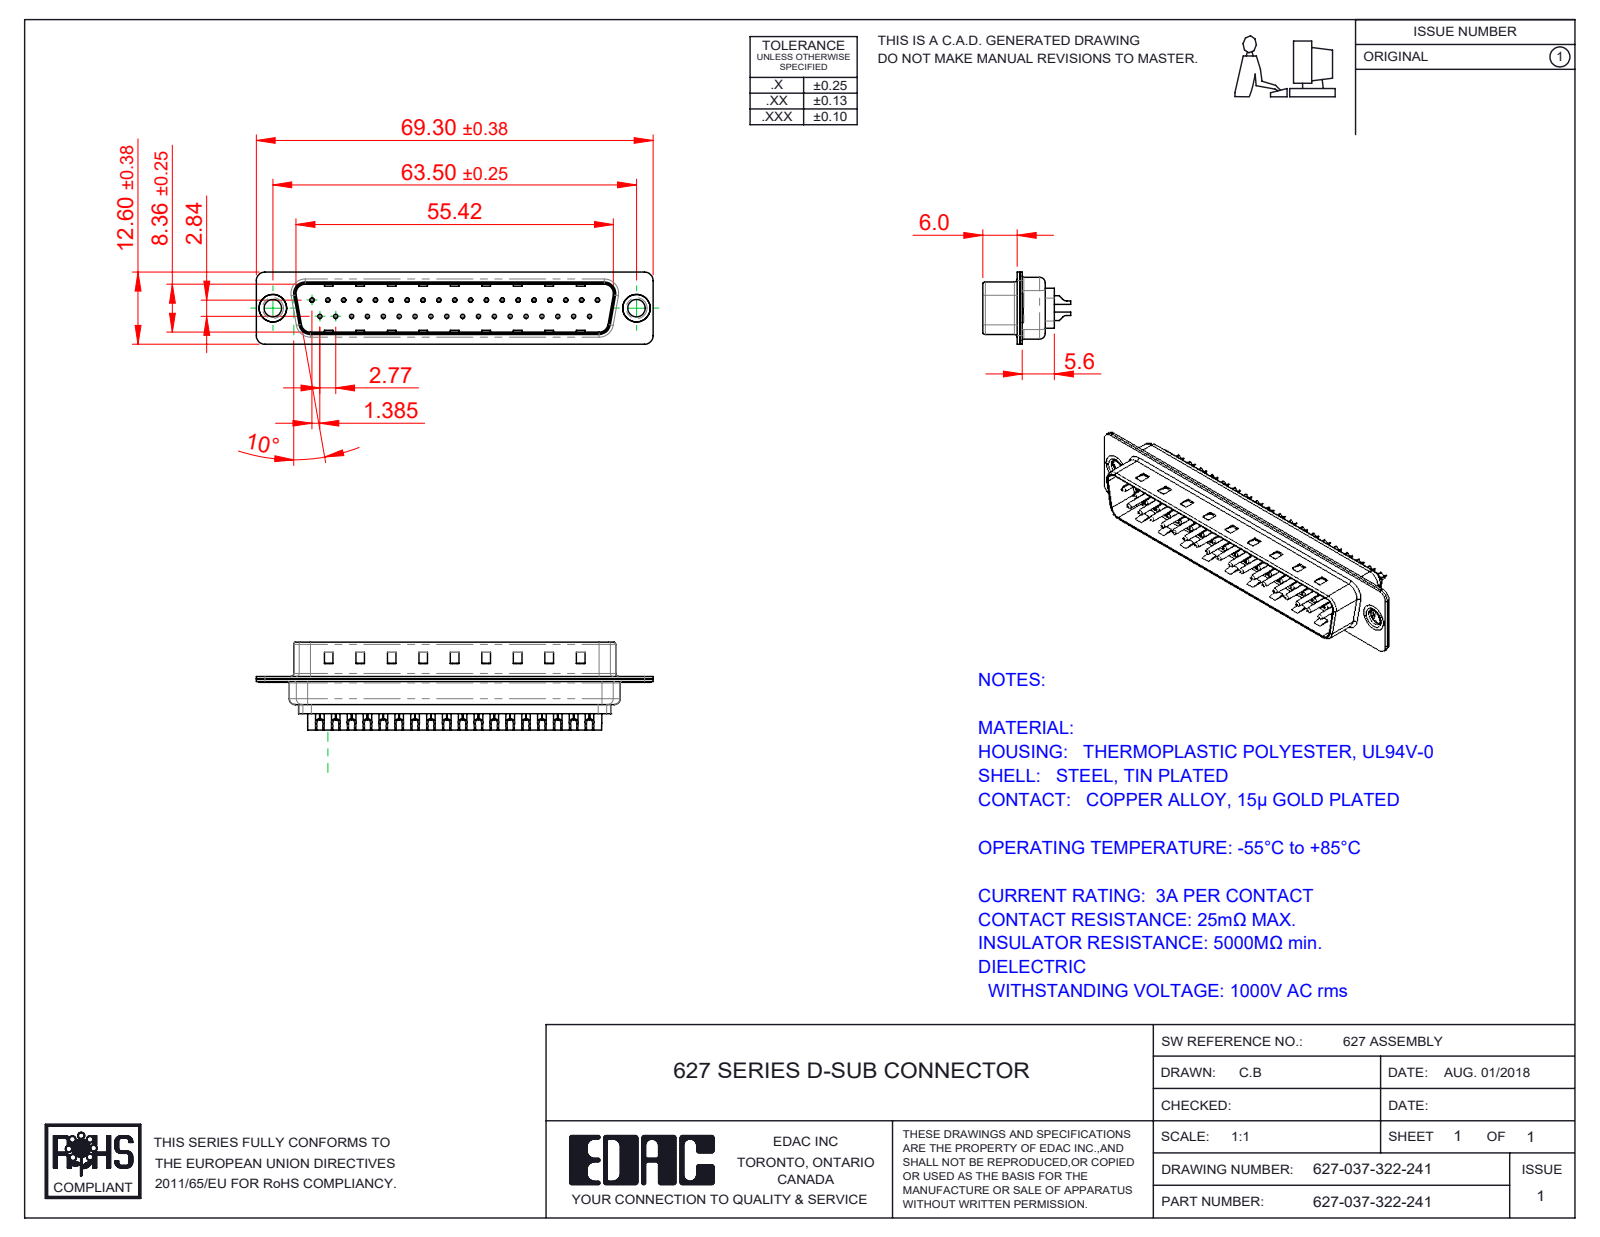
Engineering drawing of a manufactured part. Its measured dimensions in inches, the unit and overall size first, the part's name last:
Units: inches
Overall size (bounding box): 2.728 × 0.604 × 0.496
Round holes (diameter × count): ⌀0.014 ×37, ⌀0.043 ×37, ⌀0.063 ×37, ⌀0.12 ×2, ⌀0.157 ×2, ⌀0.189 ×2
Round bosses / shafts (diameter × count): ⌀0.079 ×37, ⌀0.059 ×37, ⌀0.03 ×37, ⌀0.197 ×2, ⌀0.193 ×2, ⌀0.14 ×2
Partial cylindrical surfaces — rounded edges, fillets, slot ends (radius × count): R0.059 ×16, R0.079 ×12, R0.02 ×8, R0.063 ×8, R0.039 ×6, R0.01 ×4, R0.024 ×4, R0.026 ×4
Main face-to-face distances: 0.016, 0.032, 0.377, 0.018, 0.345, 0.035, 0.059, 0.055, 0.238, 0.02
Hole centre spacings: 0.124, 0.109, 0.218, 0.327, 0.198, 0.398, 0.436, 0.503
Volume: 0.222 in³ · Surface area: 16.45 in²
Bodies: 42 solids, 2754 faces (721 planar, 1198 cylindrical, 835 other)
Part name (STEP PRODUCT): 627-037-322-041; 627 Housing_37 LP; 627 Thru Hole Rivet; 627 Contact Row 2_22L (+3 more)
STEP written by: SolidWorks 2020 (CONFIG_CONTROL_DESIGN)
